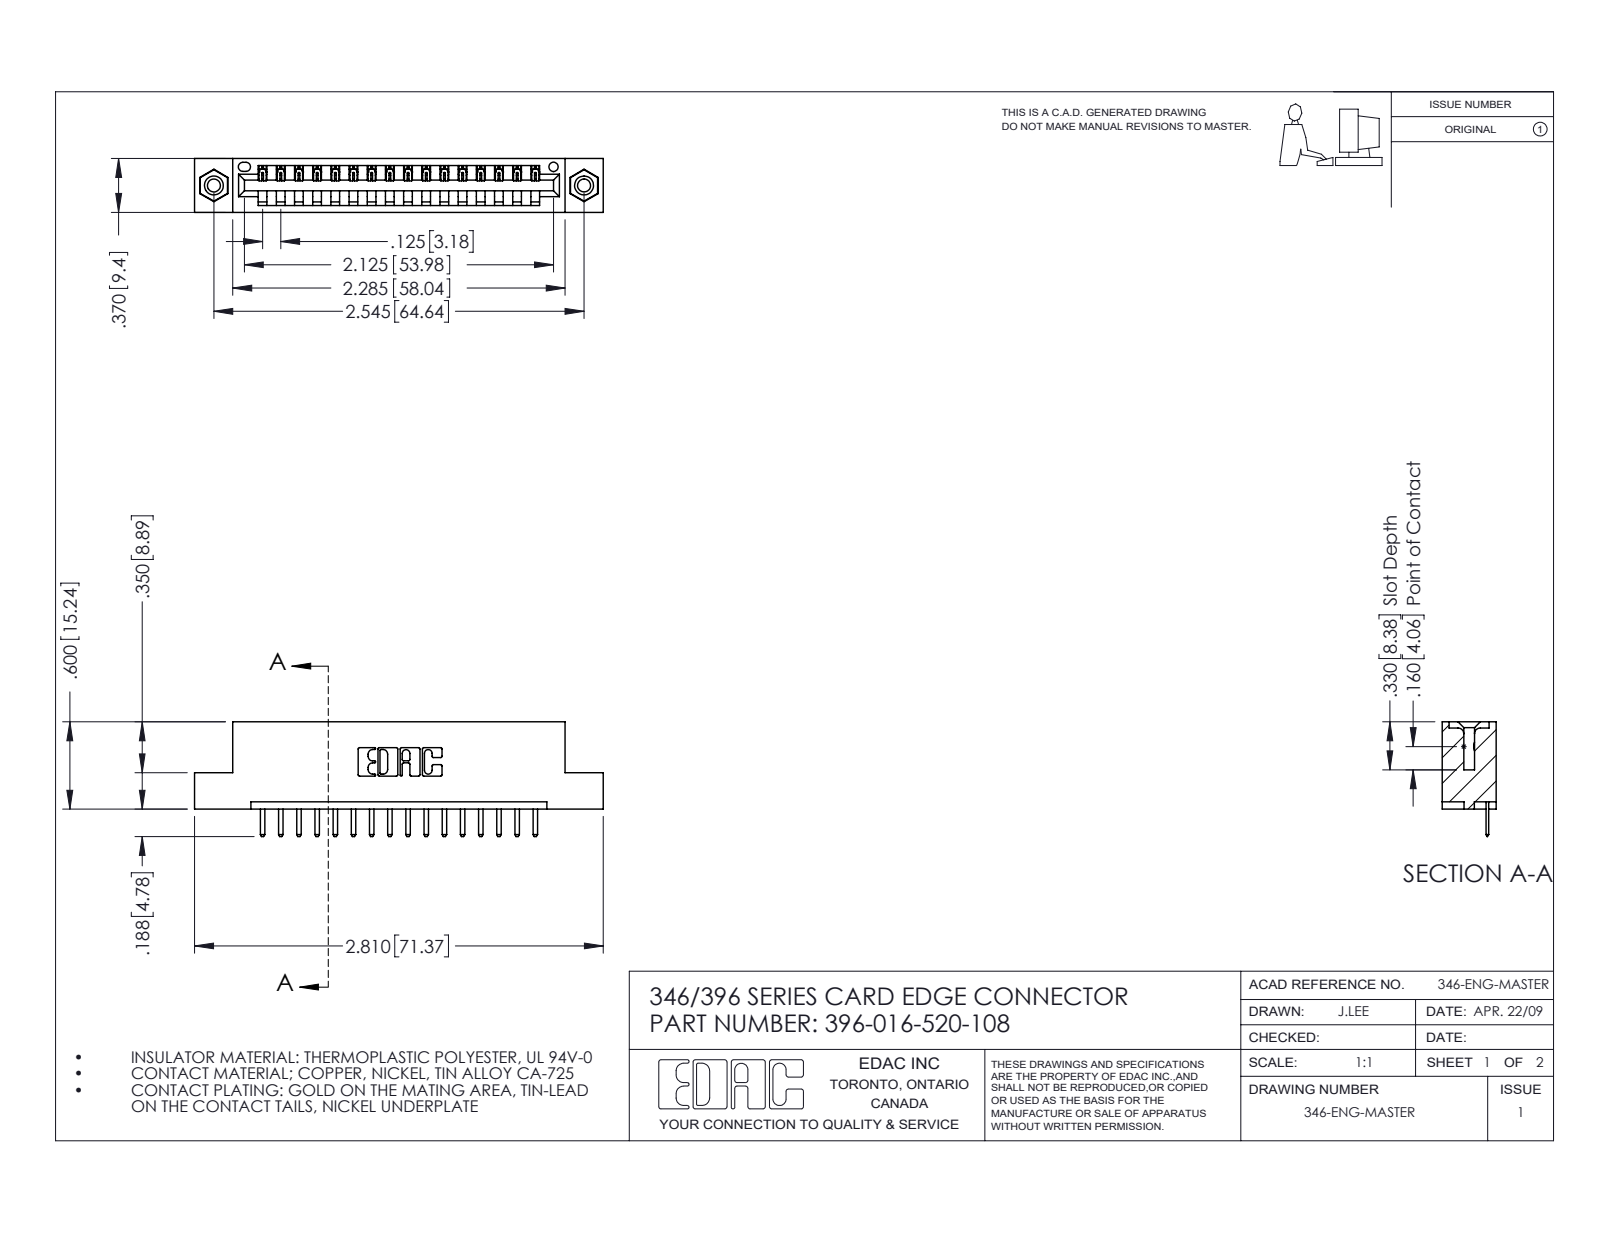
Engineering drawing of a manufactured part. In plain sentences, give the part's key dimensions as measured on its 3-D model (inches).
The part is named "345-292-001_345-293-120; 396-016-520-108; 346 Part_Flush Mounting Lugs - 0.156 Dia-TI; 345-250-001_345-250-003-102". Its 3-D file was written by "SolidWorks 2016 (CONFIG_CONTROL_DESIGN)". It is 19 solids with 1174 faces: 780 planar, 378 cylindrical and 16 other. Overall it measures 2.81 by 0.788 by 0.37 inches. Its volume is 0.403 cubic inches and its surface area 12.15 square inches. Round holes: 2 of diameter 0.089, 2 of diameter 0.125, 2 of diameter 0.156, 1 of diameter 0.064. Round bosses or shafts: 2 of diameter 0.155. Partial cylindrical surfaces (rounded edges, fillets, slot ends): 34 of radius 0.01, 32 of radius 0.006, 22 of radius 0.01, 6 of radius 0.007, 6 of radius 0.031, 3 of radius 0.026, 2 of radius 0.031, 2 of radius 0.04. The main face-to-face distances are 0.048, 0.322, 0.37, 0.25, 0.148, 0.222, 0.1, 0.174, 0.072, 0.298. The hole center spacings are 0.246, 2.338, 2.545.
